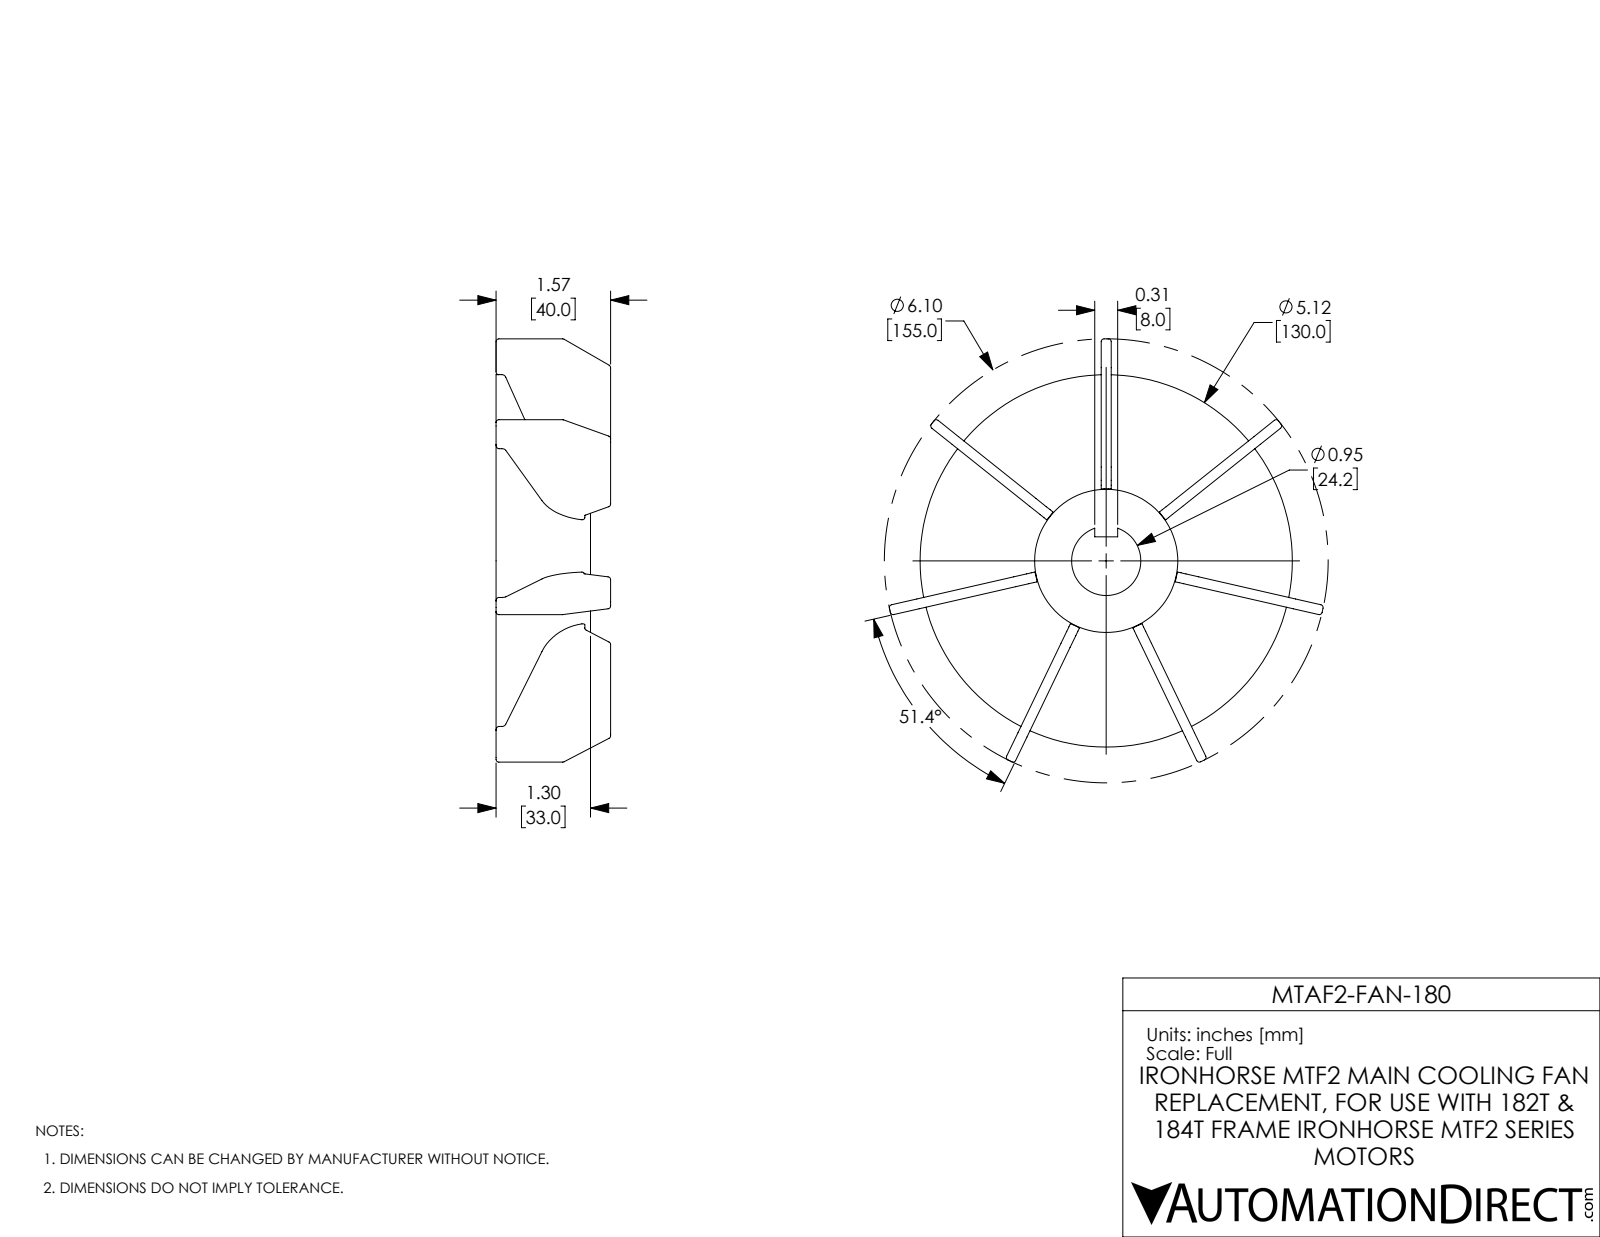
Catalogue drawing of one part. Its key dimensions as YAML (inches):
part_name: "MTAF2-FAN-180 coord norm"
step_written_by: "SolidWorks 2017 (AUTOMOTIVE_DESIGN)"
units: inches
bodies: {solids: 8, faces: 367, planar: 105, cylindrical: 158, other: 104}
overall_size: [7.108, 6.933, 1.772]
volume: 7.521
surface_area: 127.7
round_holes:
  - {diameter: 1.11, count: 1}
  - {diameter: 5.747, count: 1}
round_bosses_or_shafts:
  - {diameter: 5.906, count: 1}
  - {diameter: 1.417, count: 1}
partial_cylinders:
  - {radius: 0.059, count: 133}
  - {radius: 0.787, count: 7}
face_to_face_distances: [0.138, 0.128, 0.118, 1.457, 0.619, 0.837, 0.276, 0.344, 1.181, 0.315]
